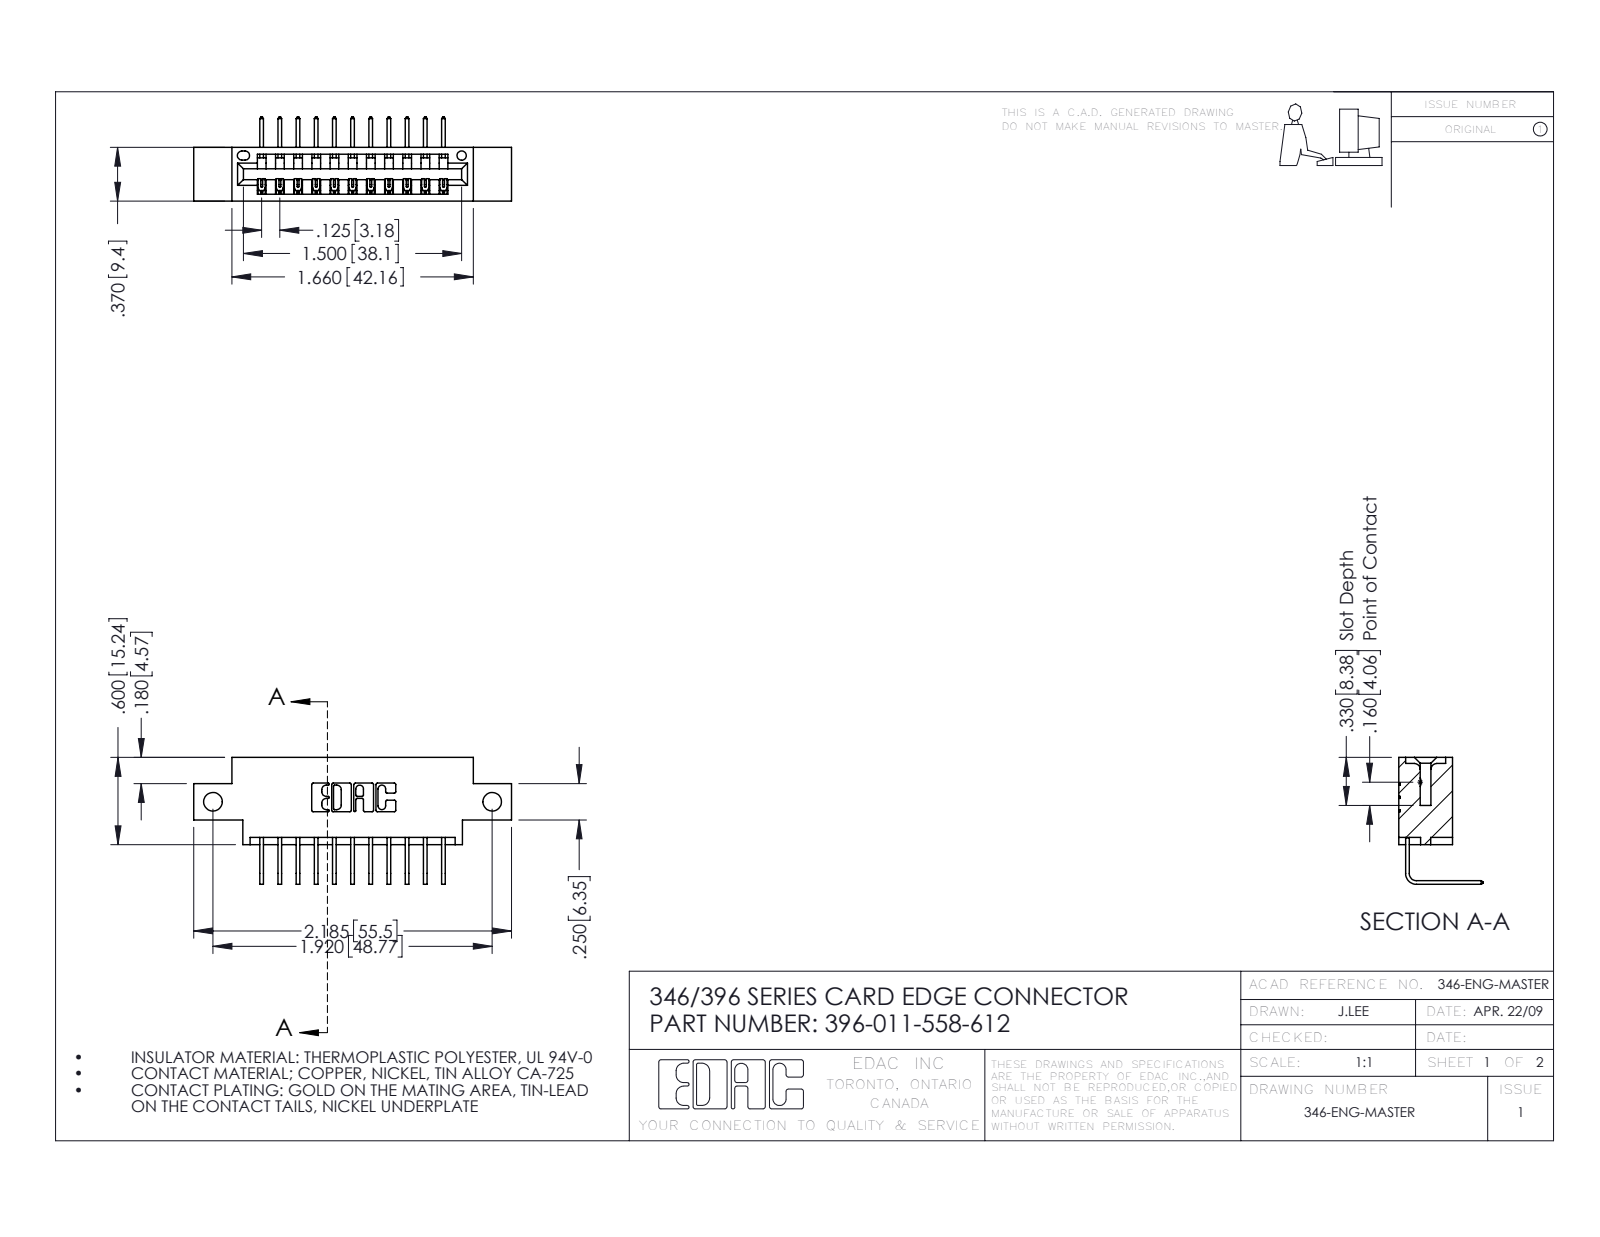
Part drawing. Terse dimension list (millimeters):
name: 346 Part_0.170 Offset - Side Mount; 345-292-001_558 Tail - 2; 396-011-558-612
written by: SolidWorks 2016 (CONFIG_CONTROL_DESIGN)
unit: mm
bodies: 12 solids, 786 faces (542 planar, 244 cylindrical, 0 other)
size: 55.5 × 22.2 × 14.7
volume: 4 900 mm³; area: 6 015 mm²
holes: 2× ⌀3.3, 1× ⌀1.6
rounds: 22× R0.2, 22× R0.3, 6× R0.2, 6× R0.8, 3× R0.7, 2× R0.8, 2× R1, 1× R0.4
face distances: 6.4, 9.4, 8.2, 1.2, 7.6, 0.6, 1.8, 3.8, 5.6, 2.5
hole spacings: 48.8
